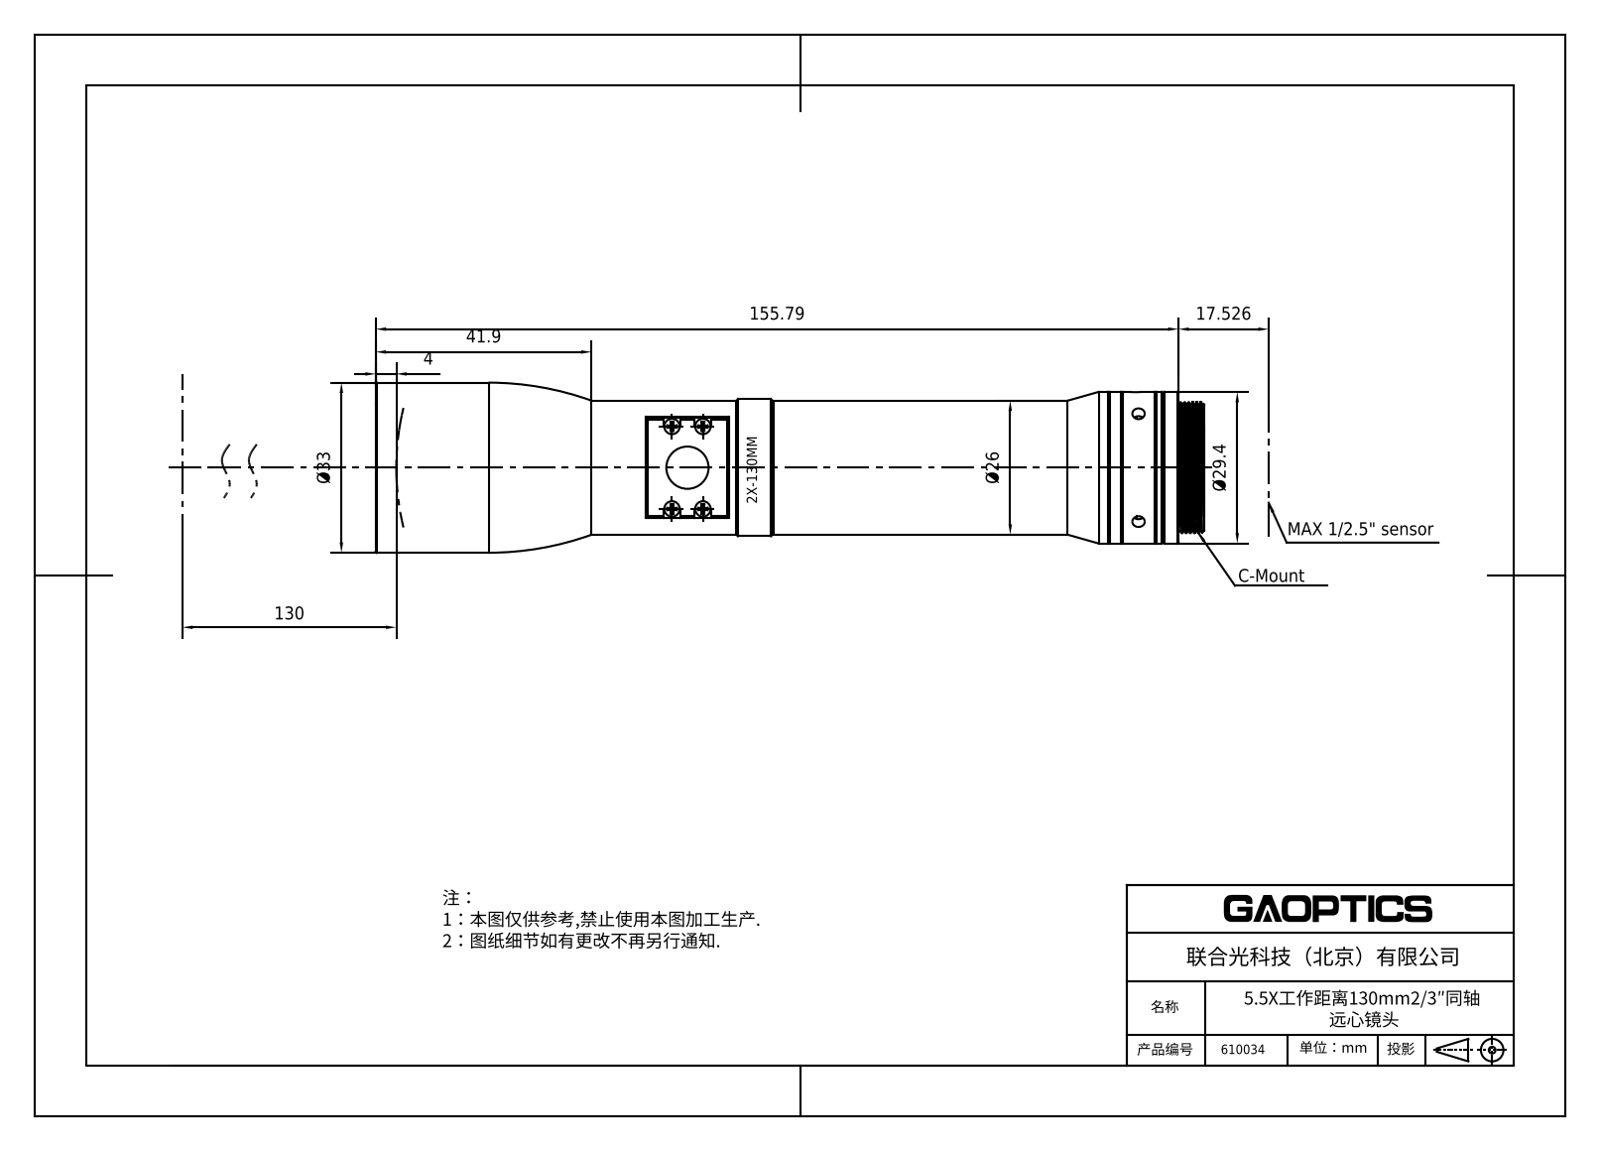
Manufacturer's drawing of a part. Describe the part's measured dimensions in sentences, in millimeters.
The part is named "610034". Its 3-D file was written by "SolidWorks 2020 (CONFIG_CONTROL_DESIGN)". It is 0 solids with 761 faces: 267 planar, 255 cylindrical and 239 other. Overall it measures 161.2 by 87.2 by 33 millimeters. Round holes: 3 of diameter 2.4, 1 of diameter 6, 1 of diameter 8, 1 of diameter 12.3, 1 of diameter 13, 1 of diameter 14, 1 of diameter 19.72, 1 of diameter 21, 1 of diameter 21.6, 1 of diameter 22, 1 of diameter 22.1, 1 of diameter 23.1. Round bosses or shafts: 5 of diameter 1.6, 4 of diameter 2.2, 1 of diameter 30.8, 1 of diameter 30.5, 1 of diameter 29.9, 1 of diameter 25.4, 1 of diameter 24.3, 1 of diameter 23.94. Partial cylindrical surfaces (rounded edges, fillets, slot ends): 4 of radius 1, 4 of radius 1.6, 1 of radius 13.22, 1 of radius 16.32. The main face-to-face distances are 2.3, 4.6, 1.5, 0.8, 3.8, 6.9, 3.1, 6.1, 9.2, 5.4. The hole center spacings are 87.54.
